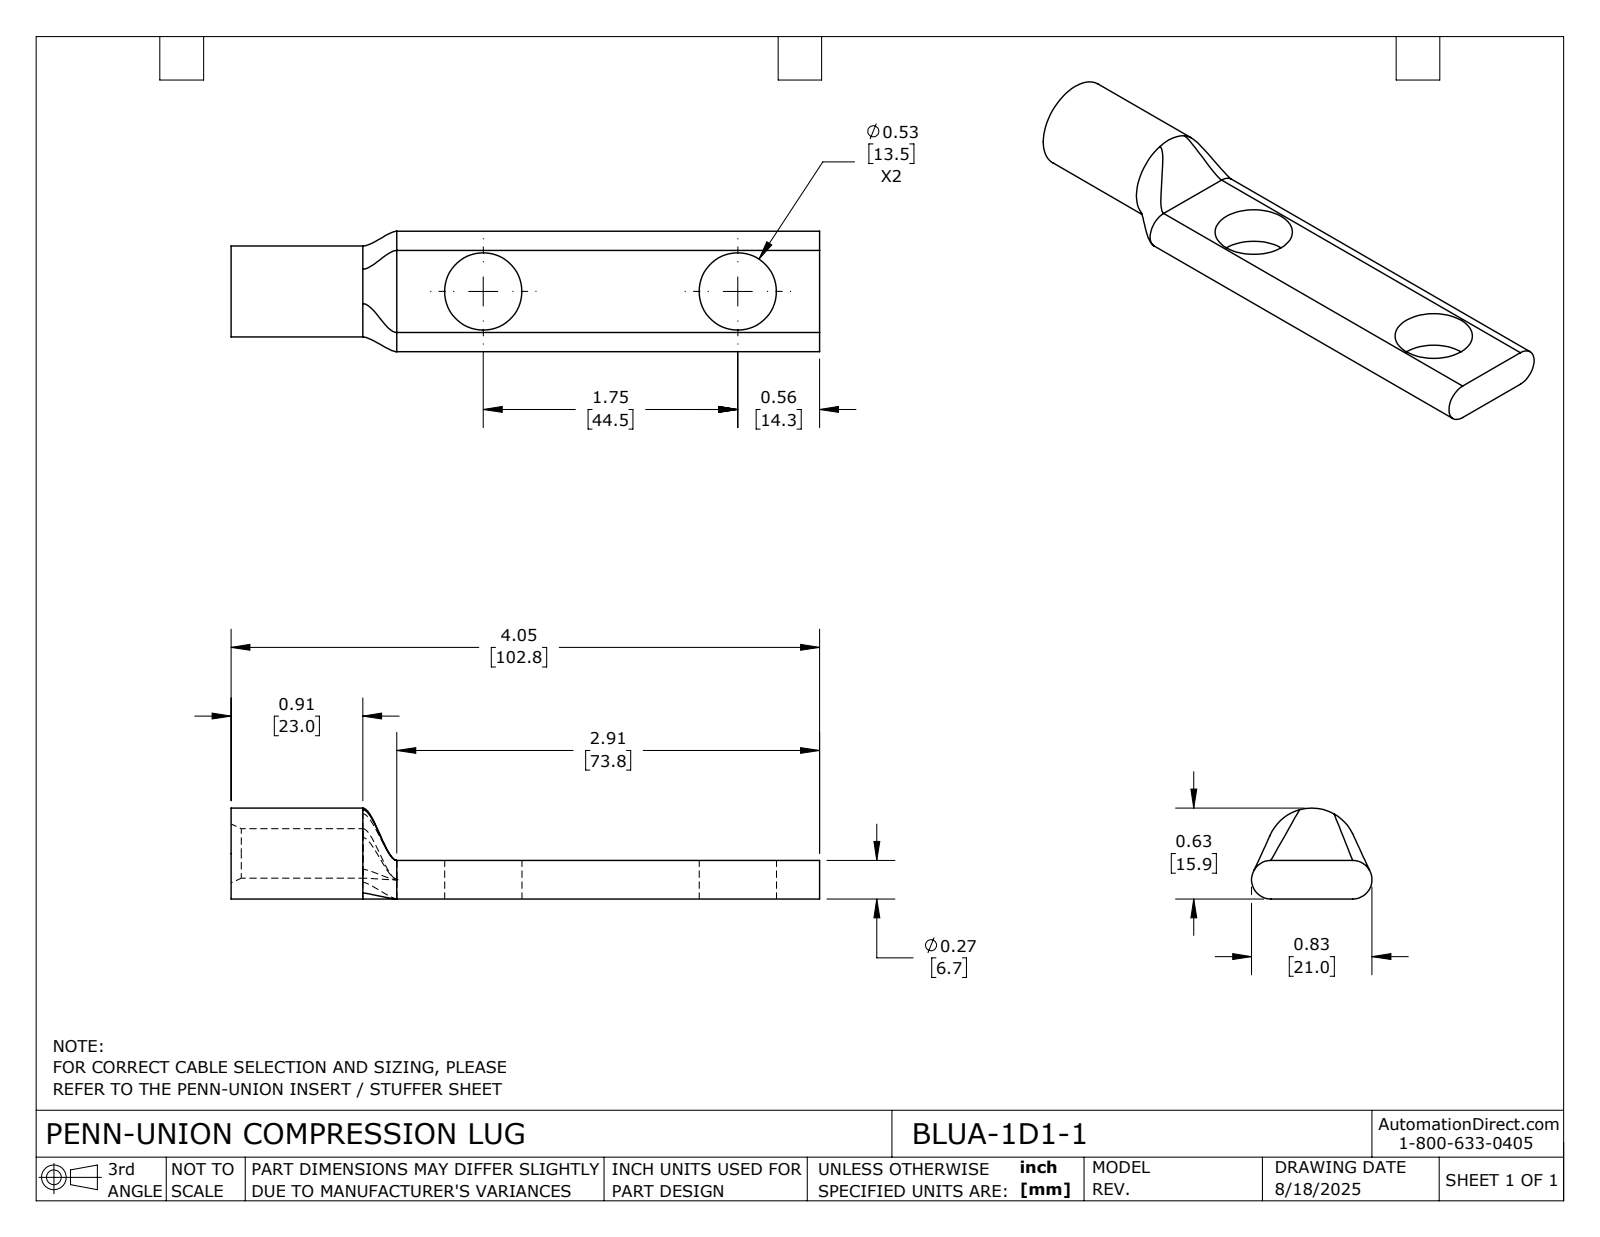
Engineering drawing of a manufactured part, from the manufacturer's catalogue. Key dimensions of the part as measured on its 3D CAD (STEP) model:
Part name (STEP PRODUCT): BLUA-1D1-1
STEP written by: SolidWorks 2024 (CONFIG_CONTROL_DESIGN)
Units: inches
Bodies: 1 solid, 26 faces (5 planar, 11 cylindrical, 10 other)
Overall size (bounding box): 4.046 × 0.828 × 0.625
Volume: 0.719 in³ · Surface area: 9.746 in²
Round holes (diameter × count): ⌀0.531 ×2, ⌀0.34 ×1
Round bosses / shafts (diameter × count): ⌀0.625 ×1
Partial cylindrical surfaces — rounded edges, fillets, slot ends (radius × count): R0.133 ×2
Main face-to-face distances: 0.265, 4.046, 1.14, 2.906
Hole centre spacings: 1.75
